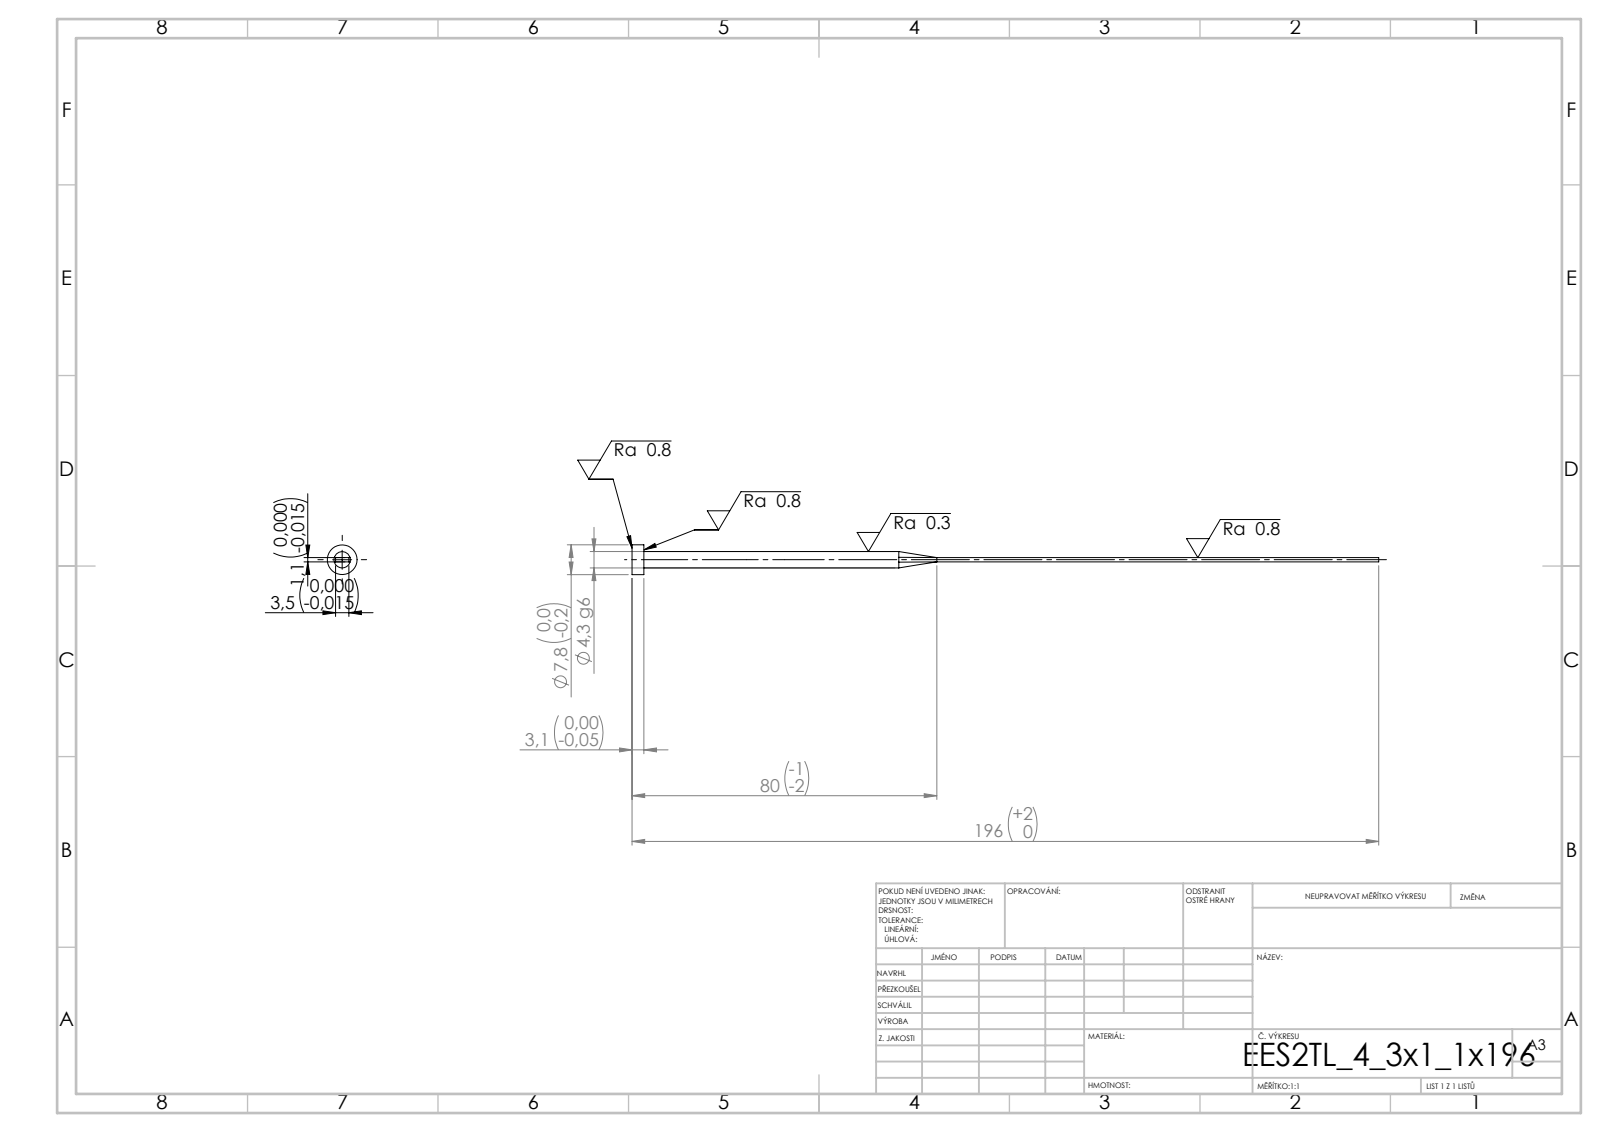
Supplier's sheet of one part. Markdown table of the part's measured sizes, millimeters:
| quantity | value |
| --- | --- |
| STEP written by | SolidWorks 2019 (CONFIG_CONTROL_DESIGN) |
| units | millimeters |
| bodies | 1 solid, 15 faces (7 planar, 4 cylindrical, 4 other) |
| overall size | 196 × 7.8 × 7.8 |
| volume | 1 653 mm³ |
| surface area | 2 242 mm² |
| round bosses / shafts (diameter × count) | 7.8 × 1, 4.3 × 1 |
| main face-to-face distances | 1.1, 3.5, 3.1, 196, 192.9 |
